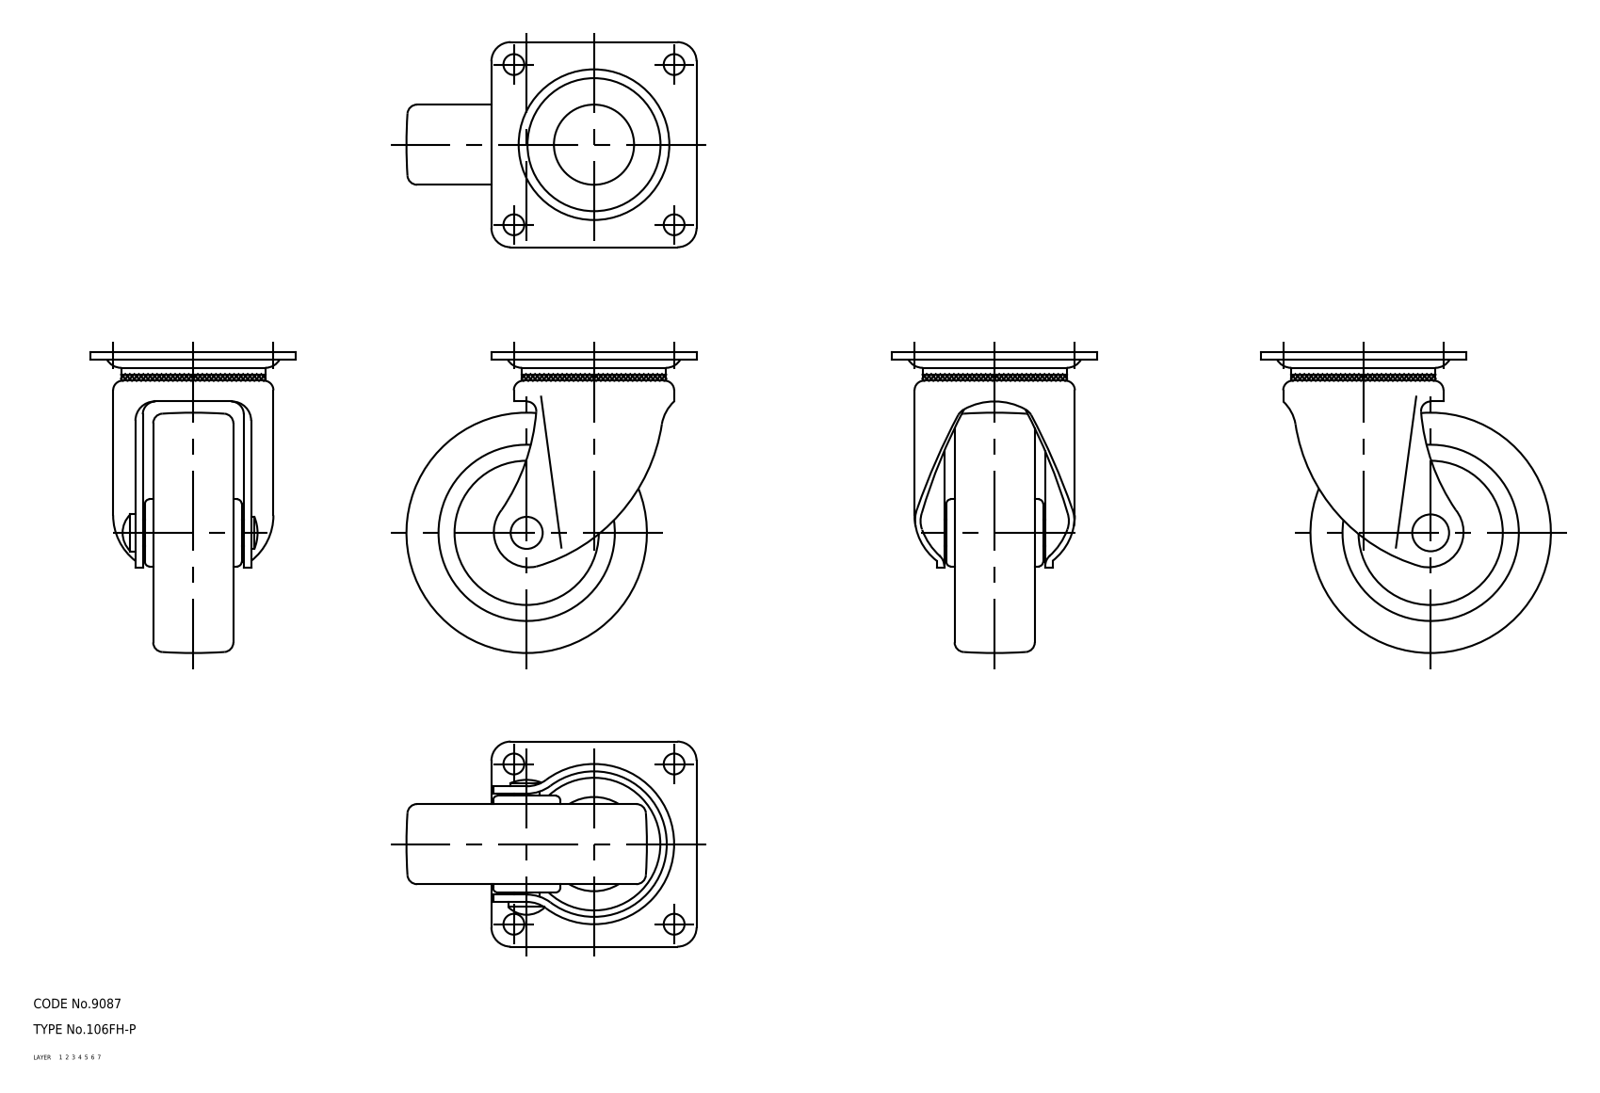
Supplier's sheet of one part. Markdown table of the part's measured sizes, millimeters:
| quantity | value |
| --- | --- |
| part name | mounting plate; wheel; main shaft; axle (+1 more) |
| STEP written by | CADfix (AUTOMOTIVE_DESIGN) |
| units | millimeters |
| bodies | 5 solids, 199 faces (0 planar, 0 cylindrical, 199 other) |
| overall size | 94 × 90.5 × 64 |
| volume | 132 560 mm³ |
| surface area | 42 731 mm² |
